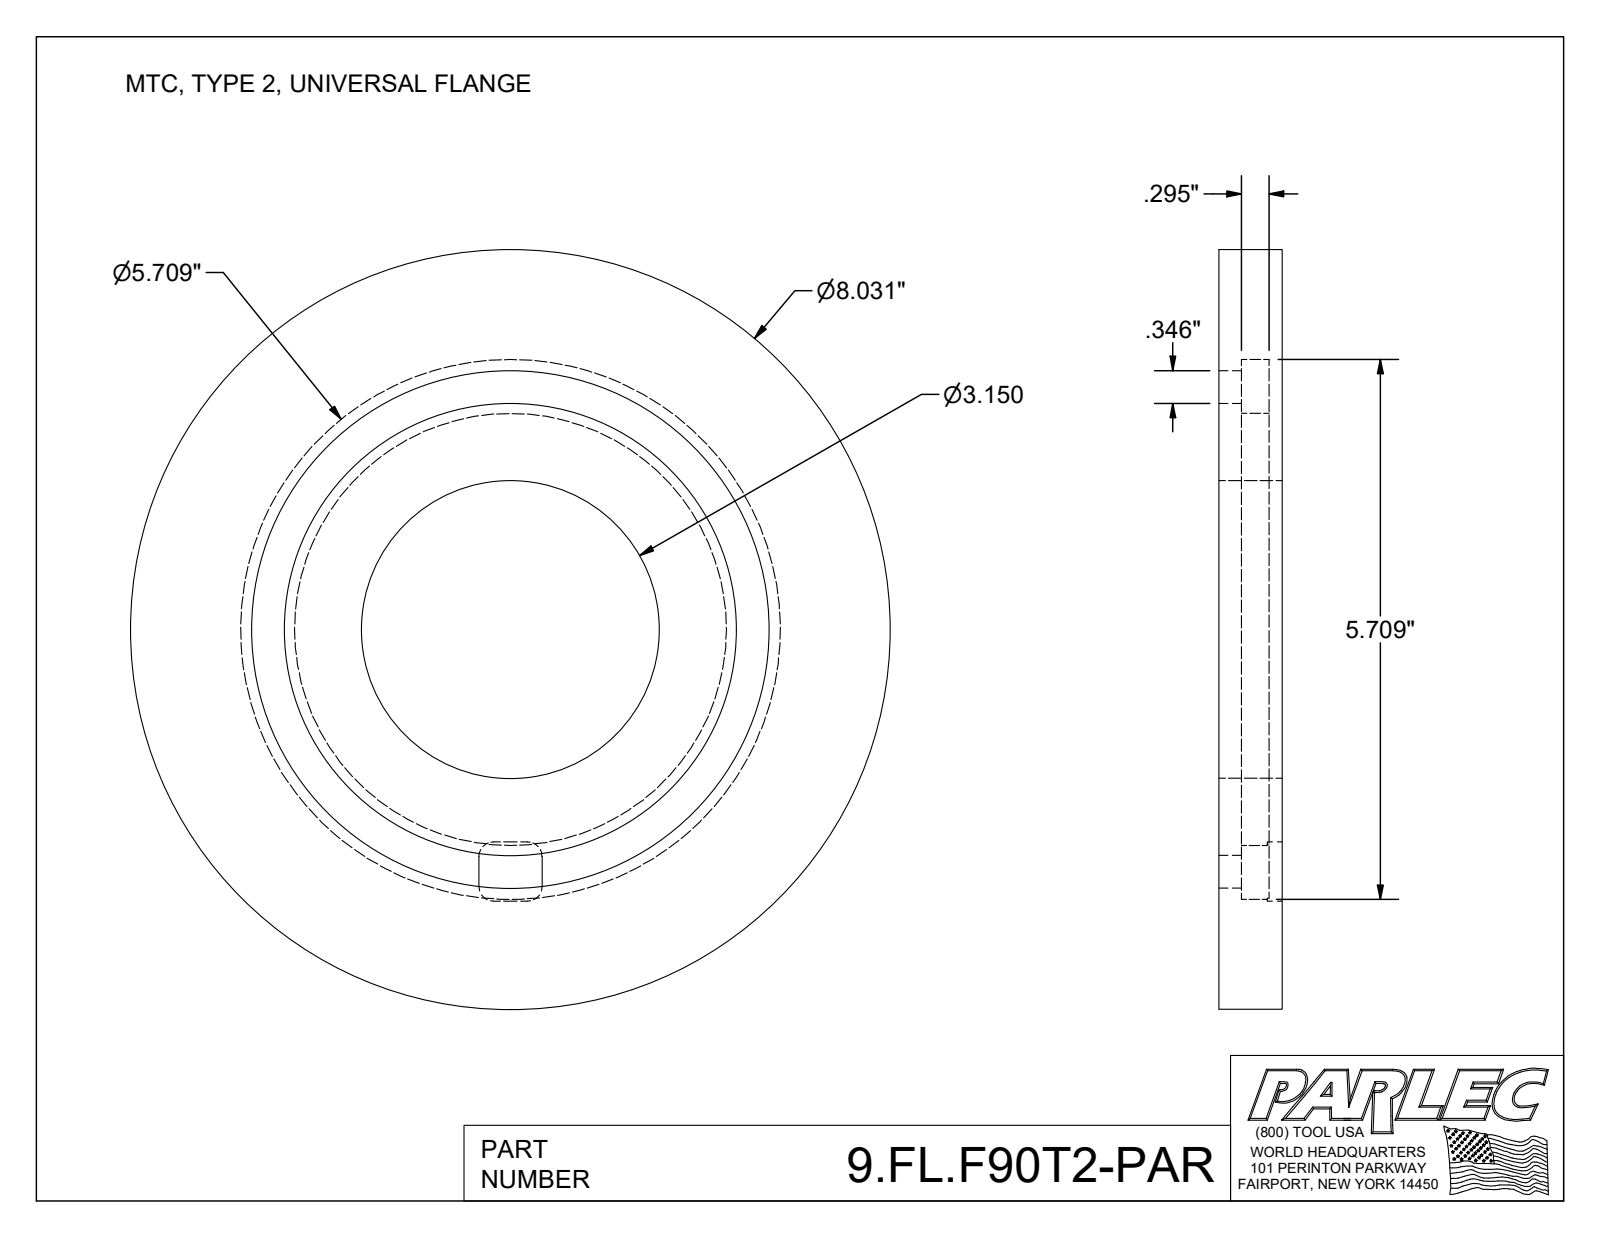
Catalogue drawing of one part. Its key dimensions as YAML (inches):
part_name: "9.FL.F90T2-PAR; 9_FL_F90T2 (MTC, Universal Flange, Type 2)"
step_written_by: "Autodesk Inventor 2022 (AUTOMOTIVE_DESIGN)"
units: inches
bodies: {solids: 1, faces: 22, planar: 12, cylindrical: 10, other: 0}
overall_size: [8.031, 8.031, 0.669]
volume: 24.6
surface_area: 133.2
round_holes:
  - {diameter: 3.15, count: 1}
  - {diameter: 5.472, count: 1}
  - {diameter: 5.709, count: 1}
round_bosses_or_shafts:
  - {diameter: 8.031, count: 1}
  - {diameter: 4.78, count: 1}
  - {diameter: 4.567, count: 1}
partial_cylinders:
  - {radius: 0.157, count: 4}
face_to_face_distances: [0.669, 0.138, 0.531, 0.433, 0.295, 0.236, 0.63, 0.157, 0.02, 0.276]
